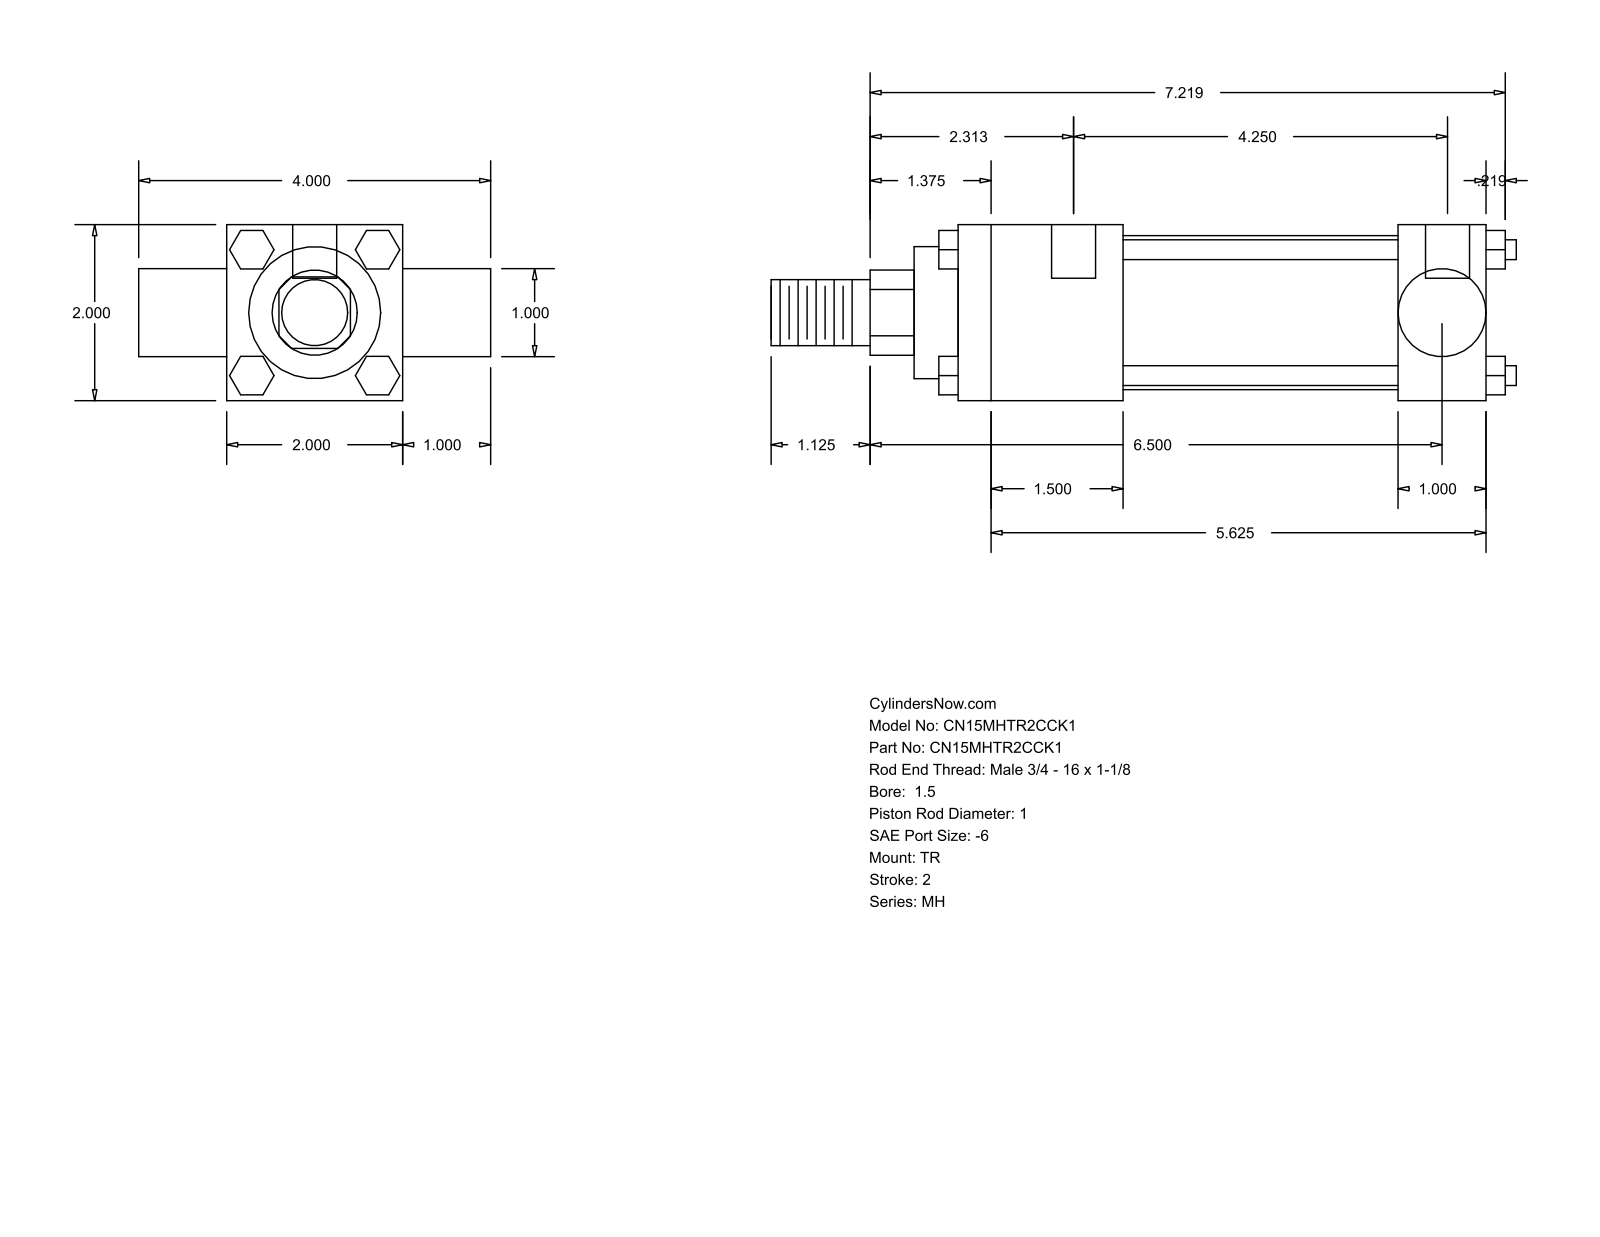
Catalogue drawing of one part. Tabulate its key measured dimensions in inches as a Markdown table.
| quantity | value |
| --- | --- |
| part name | MH_TR__0150_1 |
| STEP written by | GSSL Pune (CONFIG_CONTROL_DESIGN) |
| units | inches |
| bodies | 0 solids, 120 faces (92 planar, 28 cylindrical, 0 other) |
| overall size | 8.469 × 4 × 2 |
| round holes (diameter × count) | 0.219 × 3, 0.5 × 2 |
| round bosses / shafts (diameter × count) | 0.225 × 4, 1.75 × 1, 1.5 × 1, 1 × 1, 0.998 × 1, 0.75 × 1 |
| partial cylindrical surfaces (radius × count) | 0.484 × 1 |
| main face-to-face distances | 2, 1, 6, 3, 1.875, 4.125, 5, 3.125, 4, 0.5 |
| hole center spacings | 0.125, 4.25, 4.375 |
